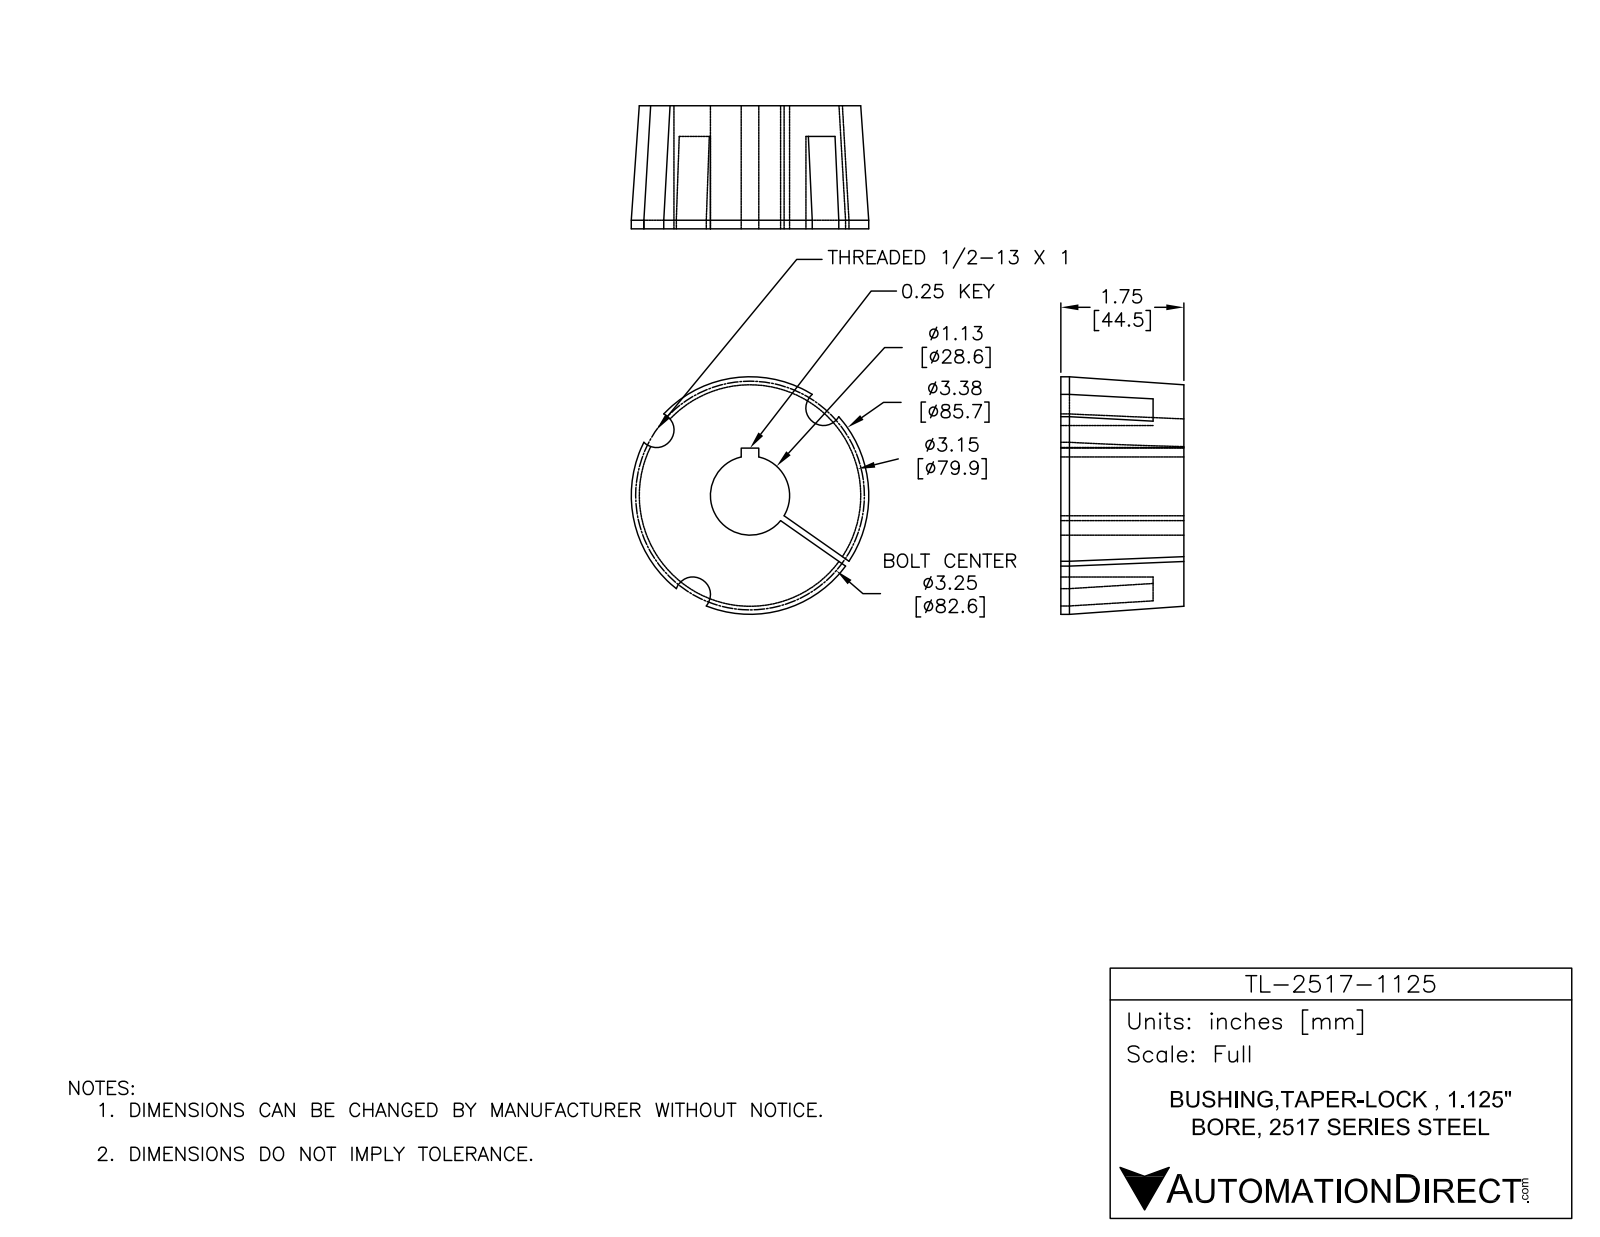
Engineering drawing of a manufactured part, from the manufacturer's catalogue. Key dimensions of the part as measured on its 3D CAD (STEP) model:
Part name (STEP PRODUCT): TL-2517-1125
STEP written by: SolidWorks 2014 (AUTOMOTIVE_DESIGN)
Units: inches
Bodies: 1 solid, 25 faces (9 planar, 13 cylindrical, 3 other)
Overall size (bounding box): 3.375 × 3.375 × 1.75
Volume: 12.29 in³ · Surface area: 43.56 in²
Round holes (diameter × count): ⌀1.125 ×1
Round bosses / shafts (diameter × count): ⌀3.375 ×1
Partial cylindrical surfaces — rounded edges, fillets, slot ends (radius × count): R0.25 ×3
Main face-to-face distances: 1.75, 0.085, 0.25, 0.437, 1.313
